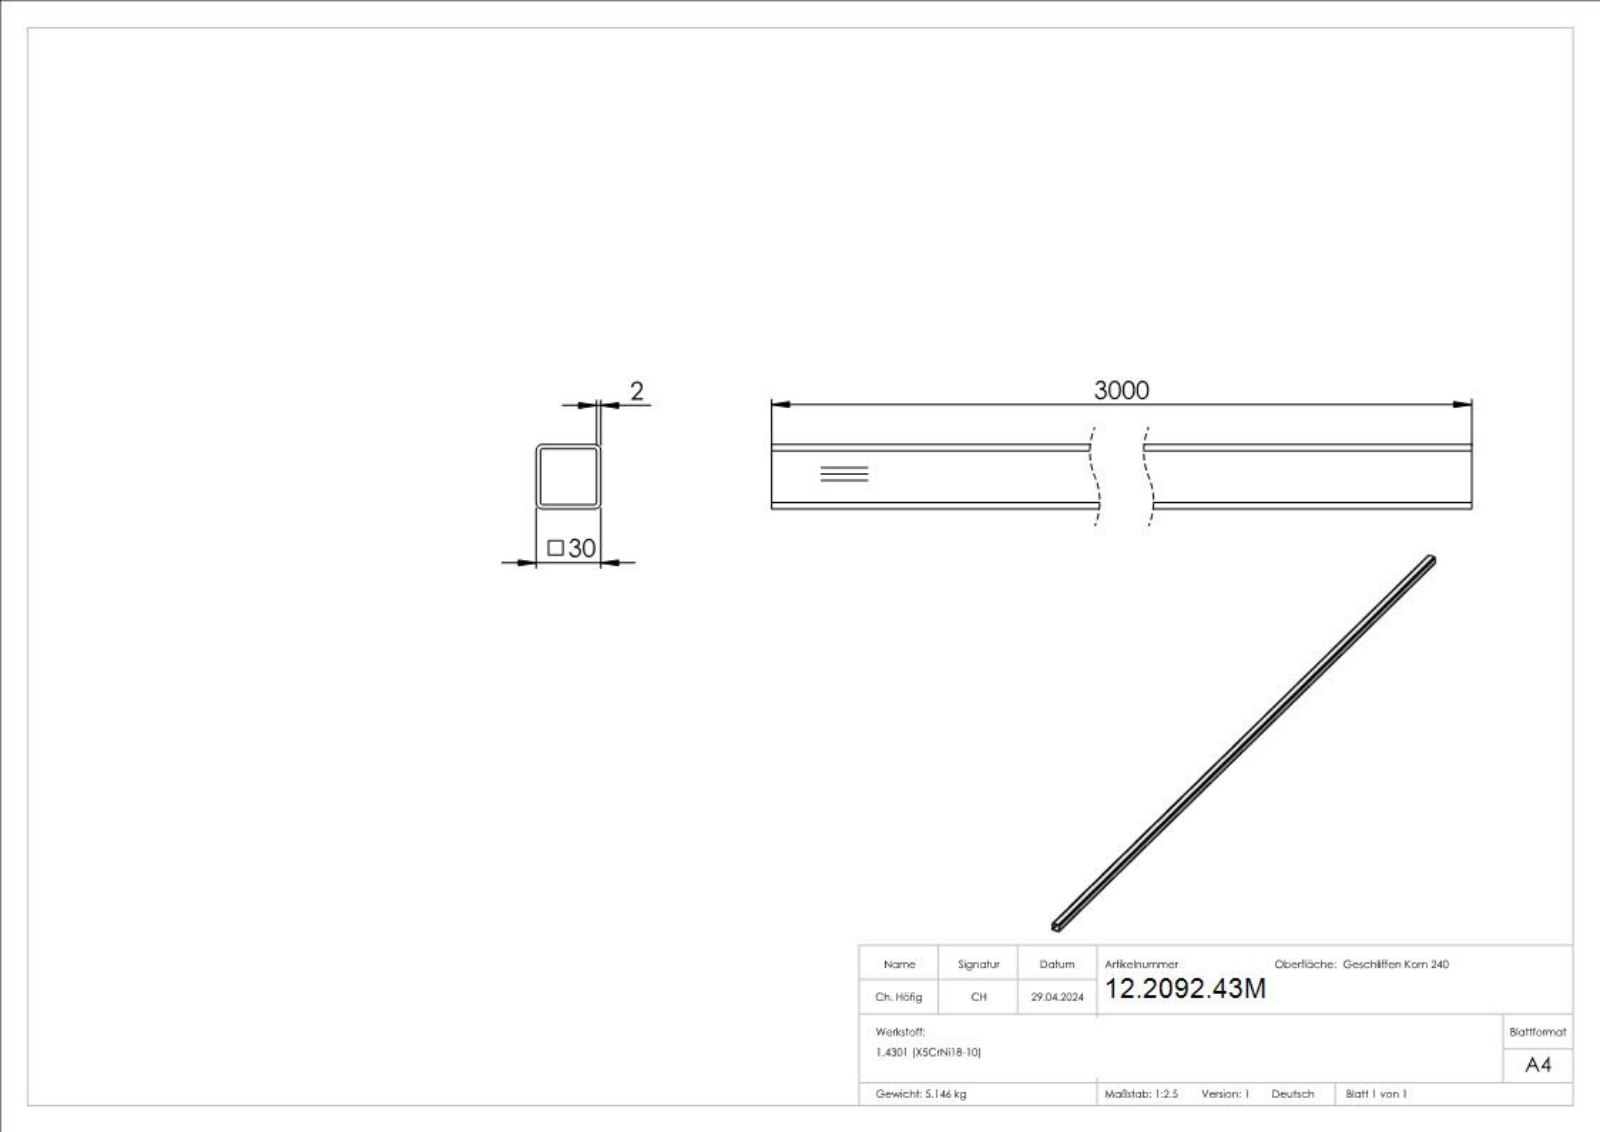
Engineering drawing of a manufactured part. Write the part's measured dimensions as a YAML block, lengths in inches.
part_name: "55399-2403M"
step_written_by: "SolidWorks 2018 (CONFIG_CONTROL_DESIGN)"
units: inches
bodies: {solids: 1, faces: 326, planar: 173, cylindrical: 8, other: 145}
overall_size: [118.11, 1.181, 1.181]
volume: 39.75
surface_area: 1010
partial_cylinders:
  - {radius: 0.039, count: 4}
  - {radius: 0.118, count: 4}
face_to_face_distances: [0.079, 1.102, 1.181, 1.024, 118.11, 0.075, 1.028, 1.106, 0.035, 0.106]
